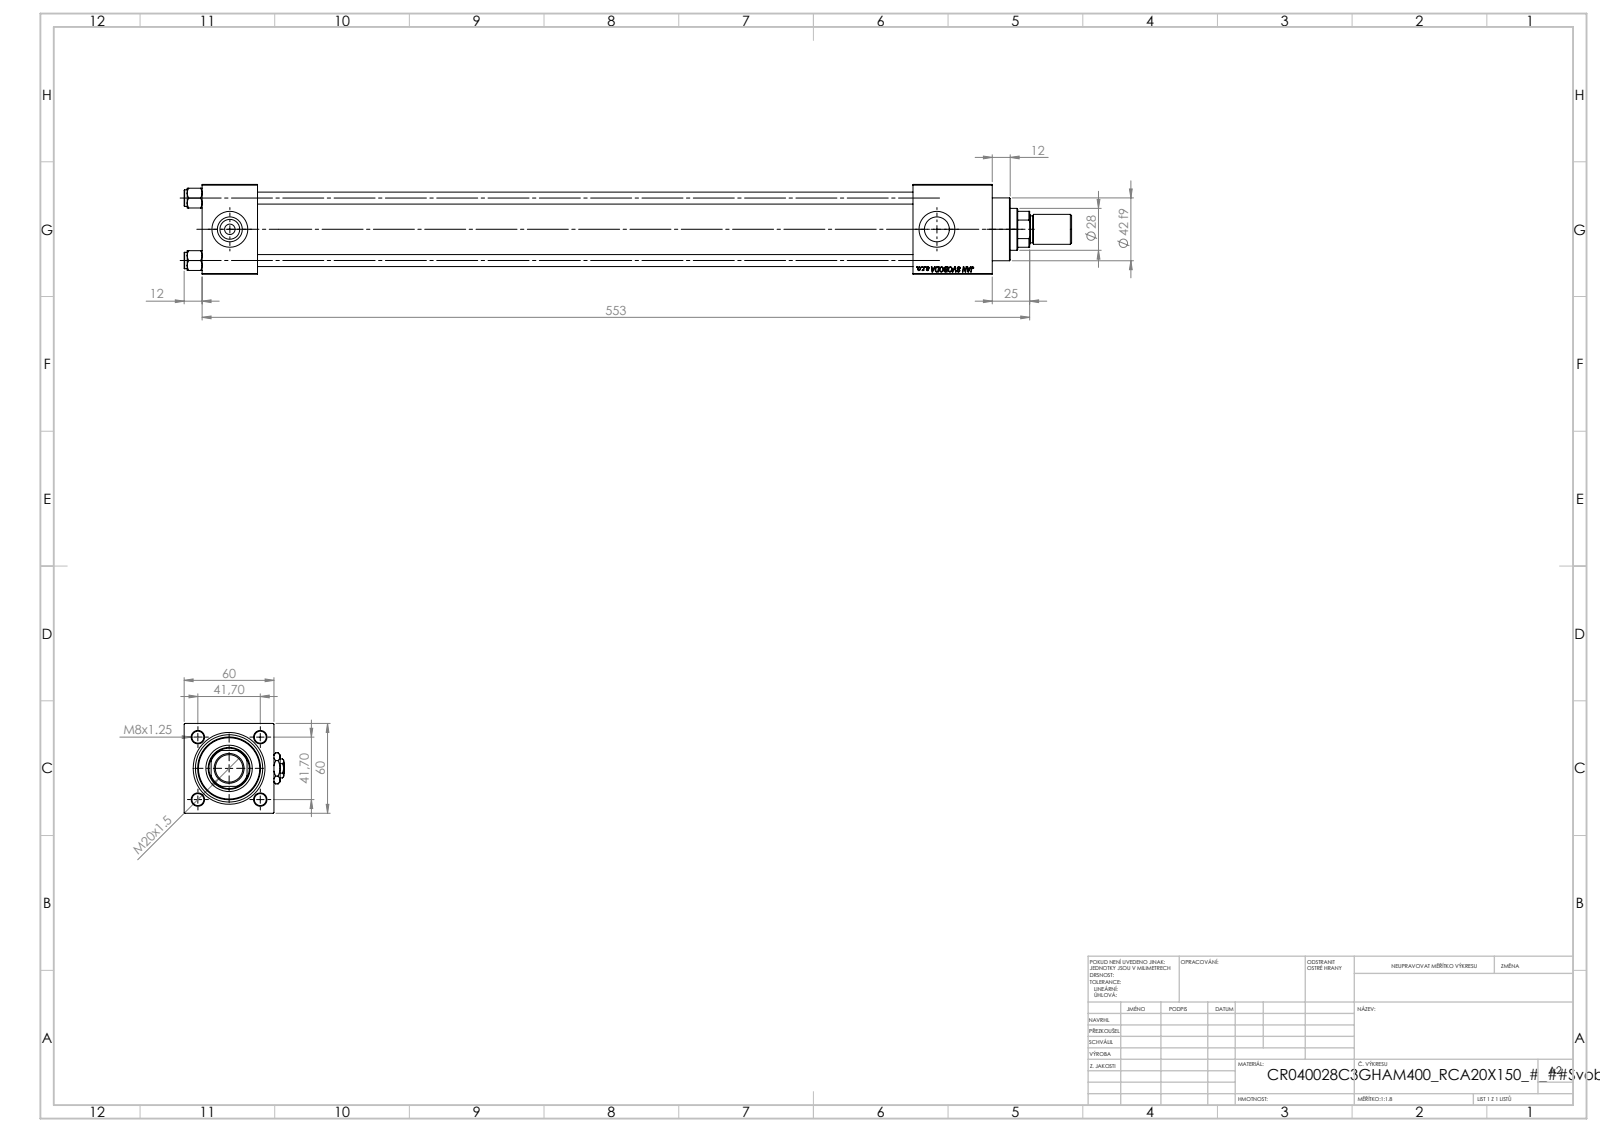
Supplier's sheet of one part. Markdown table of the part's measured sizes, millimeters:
| quantity | value |
| --- | --- |
| part name | NUT_M5_C; V215_VC_A; V215CR_C_TYCINKA; V215CR_C_Body (+3 more) |
| STEP written by | SolidWorks 2019 (CONFIG_CONTROL_DESIGN) |
| units | millimeters |
| bodies | 14 solids, 1264 faces (578 planar, 102 cylindrical, 584 other) |
| overall size | 593 × 67 × 60 |
| volume | 893 981 mm³ |
| surface area | 291 079 mm² |
| round holes (diameter × count) | 8 × 4, 7 × 2, 16.66 × 2, 24 × 2, 18.5 × 1, 28 × 1, 31 × 1, 40 × 1, 45 × 1 |
| round bosses / shafts (diameter × count) | 11 × 4, 46 × 1, 42 × 1, 20 × 1, 18 × 1 |
| partial cylindrical surfaces (radius × count) | 13.5 × 1 |
| main face-to-face distances | 60, 37, 475, 438, 53, 499.3, 462.3, 24.3, 528, 491 |
| hole center spacings | 29.49, 41.7, 58.97, 472.5 |
